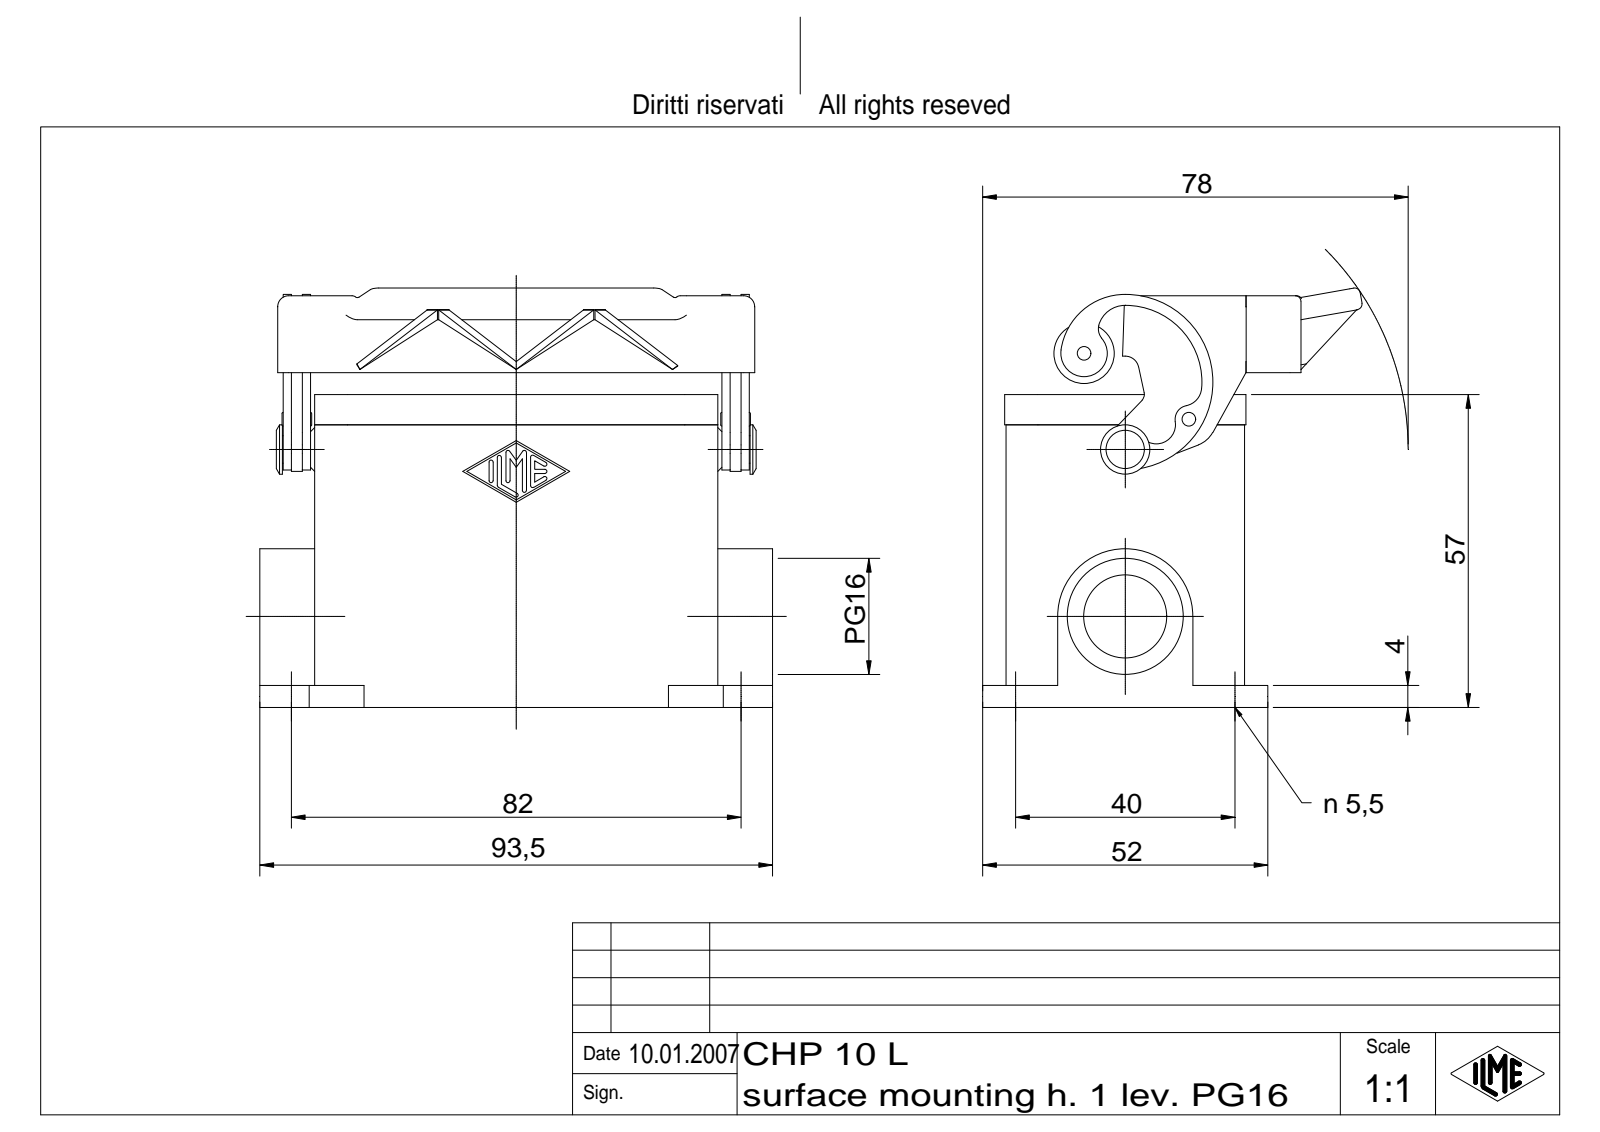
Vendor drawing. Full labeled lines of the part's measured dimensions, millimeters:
Part name (STEP PRODUCT): CHP 10 L
STEP written by: Autodesk Inventor 7 (AUTOMOTIVE_DESIGN)
Units: millimetres
Bodies: 4 solids, 432 faces (164 planar, 123 cylindrical, 145 other)
Overall size (bounding box): 93.5 × 76.42 × 69.2
Volume: 85 404 mm³ · Surface area: 46 845 mm²
Round holes (diameter × count): ⌀5.5 ×4, ⌀2 ×1, ⌀15.16 ×1, ⌀21.16 ×1
Round bosses / shafts (diameter × count): ⌀11 ×1, ⌀9 ×1, ⌀5 ×1, ⌀3 ×1, ⌀2.5 ×1
Partial cylindrical surfaces — rounded edges, fillets, slot ends (radius × count): R0.38 ×14, R2 ×12, R6 ×8, R1 ×7, R1.5 ×5, R3 ×4, R2.5 ×3, R3.5 ×2
Main face-to-face distances: 3, 40.5, 4, 43.5, 37.5, 11.75, 8.75, 61.75, 51.5, 47.5
Hole centre spacings: 40, 82, 91.24, 37.75
